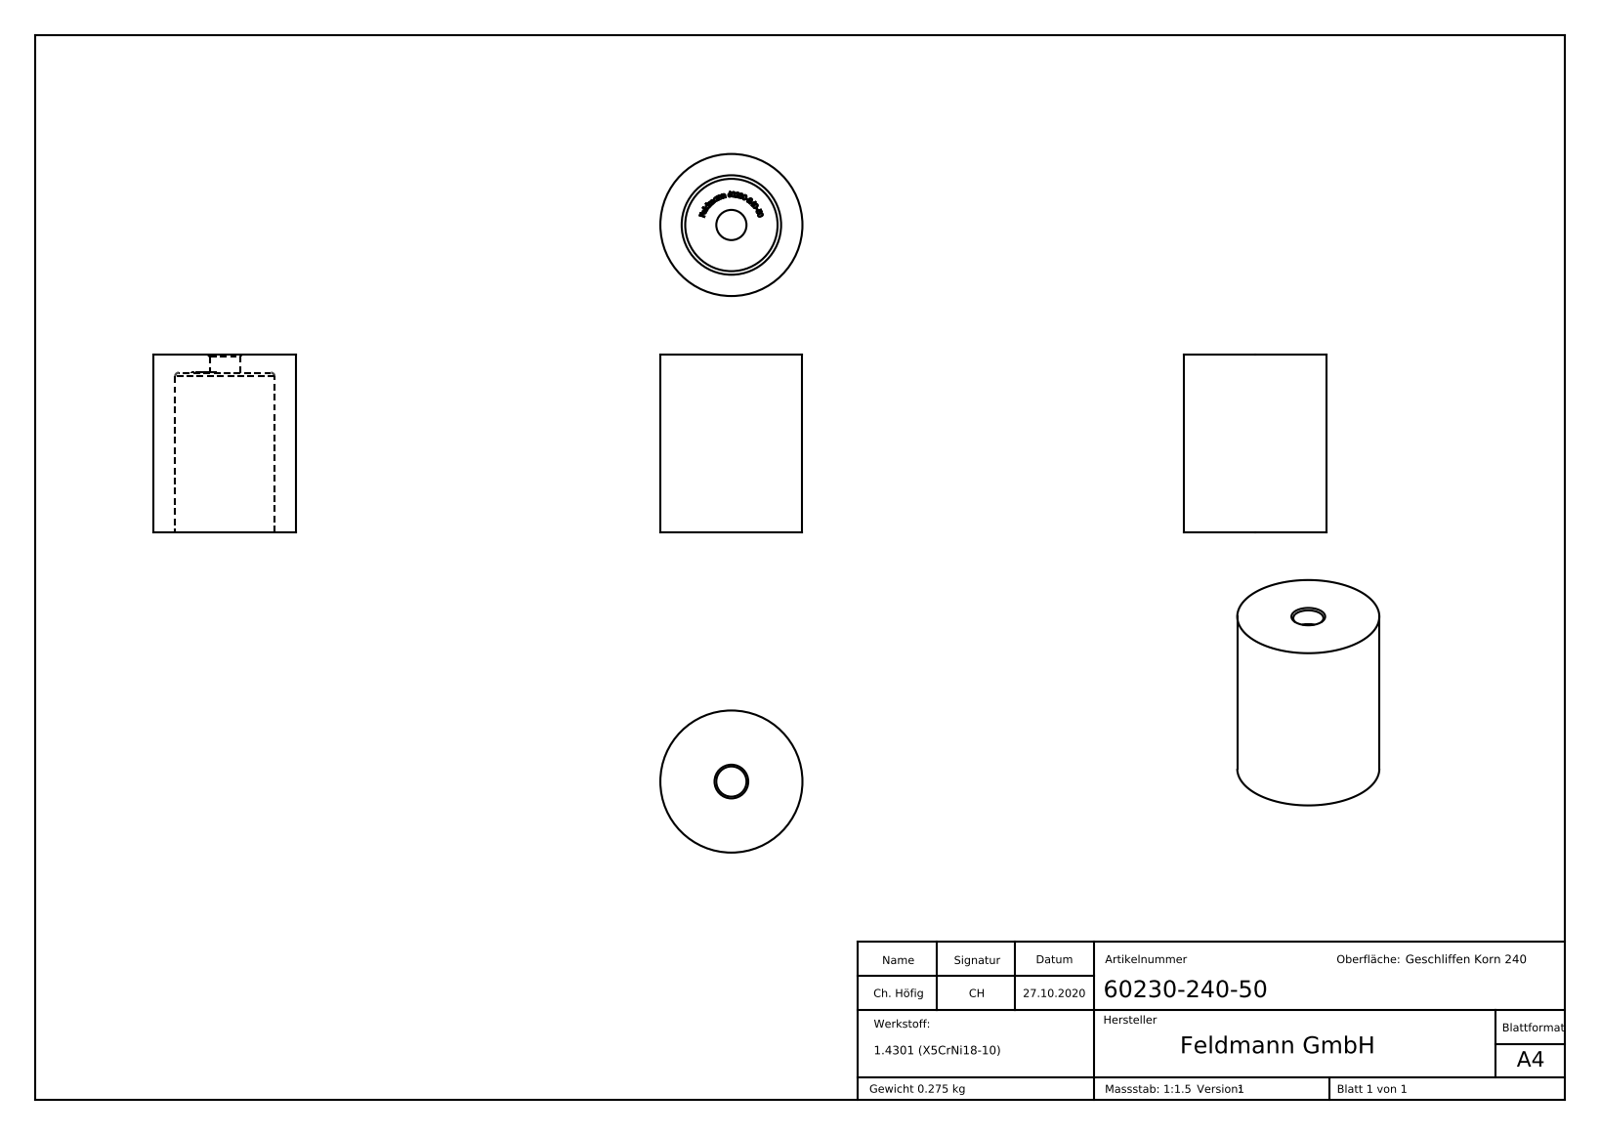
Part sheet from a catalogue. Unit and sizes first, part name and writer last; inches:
Units: inches
Overall size (bounding box): 1.969 × 1.575 × 1.575
Round holes (diameter × count): ⌀0.335 ×1, ⌀1.102 ×1
Round bosses / shafts (diameter × count): ⌀1.575 ×1
Main face-to-face distances: 1.969, 1.772, 0.197, 1.776, 0.193, 0.021, 0.026, 0.028, 0.026, 0.024
Volume: 2.127 in³ · Surface area: 19.75 in²
Bodies: 1 solid, 268 faces (131 planar, 6 cylindrical, 131 other)
Part name (STEP PRODUCT): 60230-240-50
STEP written by: SolidWorks 2018 (CONFIG_CONTROL_DESIGN)
